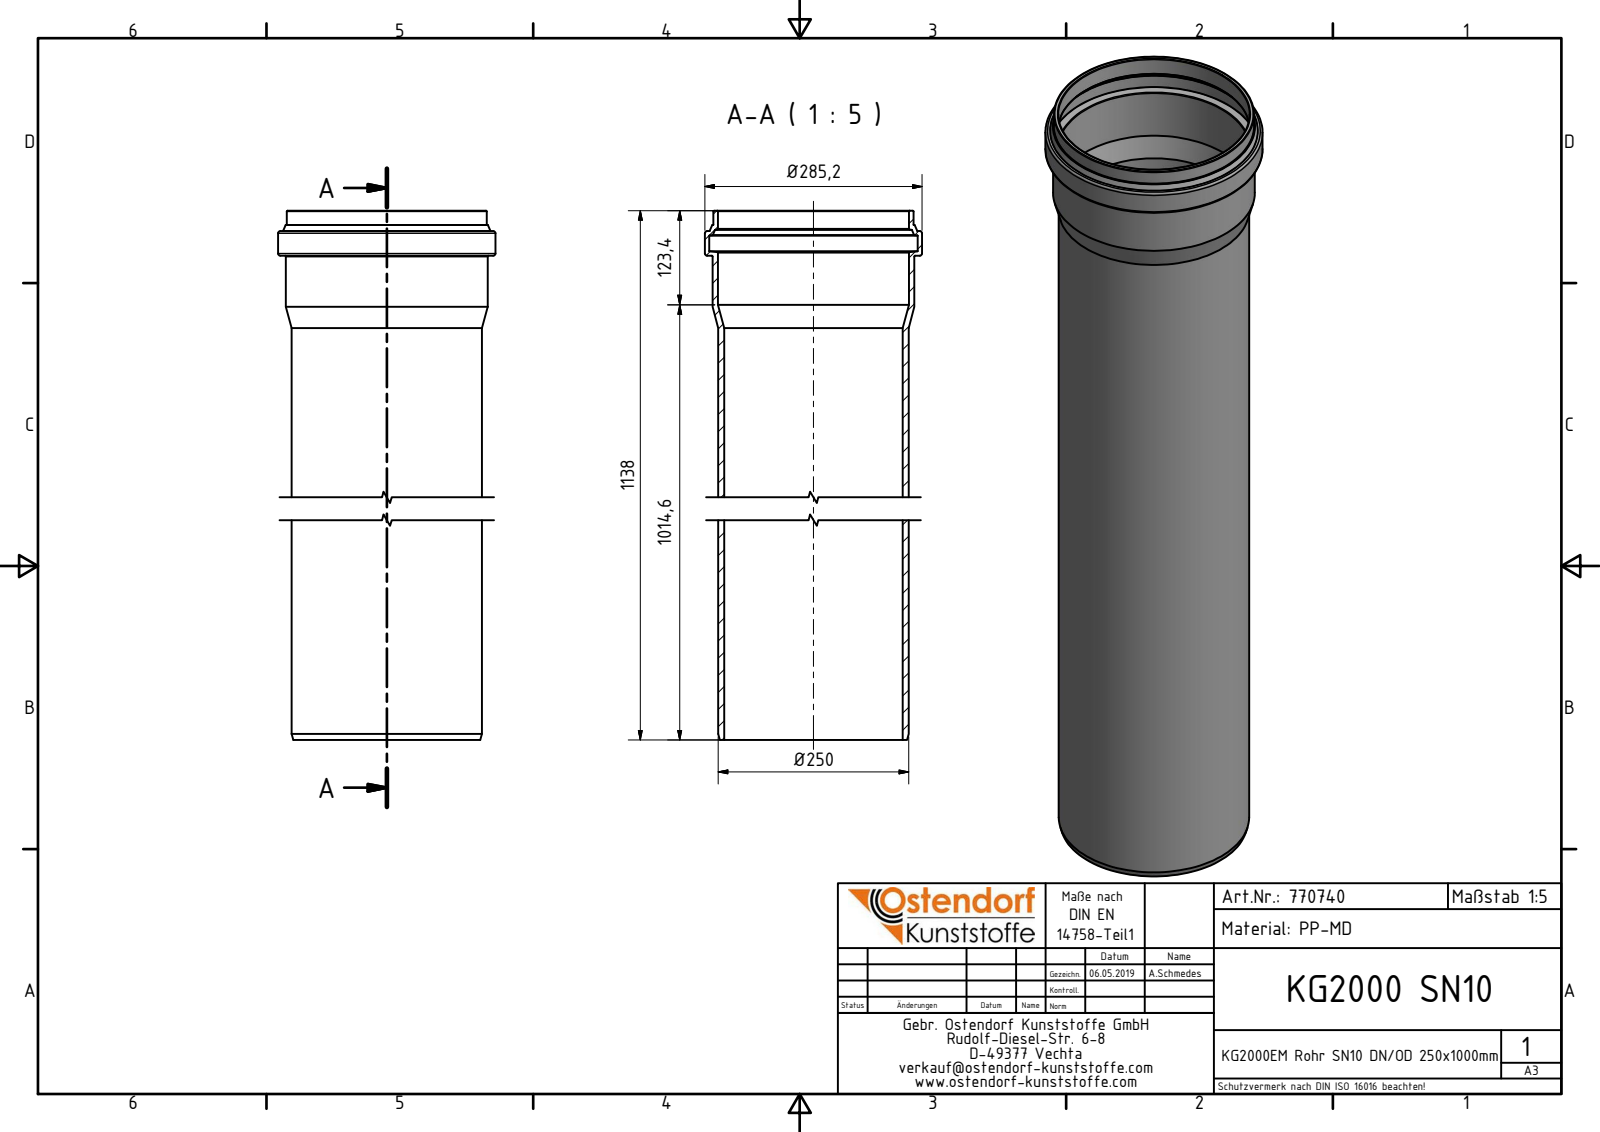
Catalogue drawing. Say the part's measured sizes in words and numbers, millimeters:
The part is named "770740 KG2000EM Rohr SN10 DN-OD250x1000". Its 3-D file was written by "Autodesk Inventor 2016 (AUTOMOTIVE_DESIGN)". It is 1 solid with 35 faces: 5 planar, 8 cylindrical and 22 other. Overall it measures 1138 by 285.2 by 285.2 millimeters. Its volume is 6 687 000 cubic millimeters and its surface area 1 787 000 square millimeters. Round holes: 1 of diameter 234.6, 1 of diameter 251, 1 of diameter 273.6. Round bosses or shafts: 1 of diameter 285.2, 1 of diameter 265, 1 of diameter 262.6, 1 of diameter 250. The main face-to-face distances are 1078.8, 1138, 59.2, 1111.3, 32.5, 26.7, 1119.13, 40.33, 7.83, 18.87.
